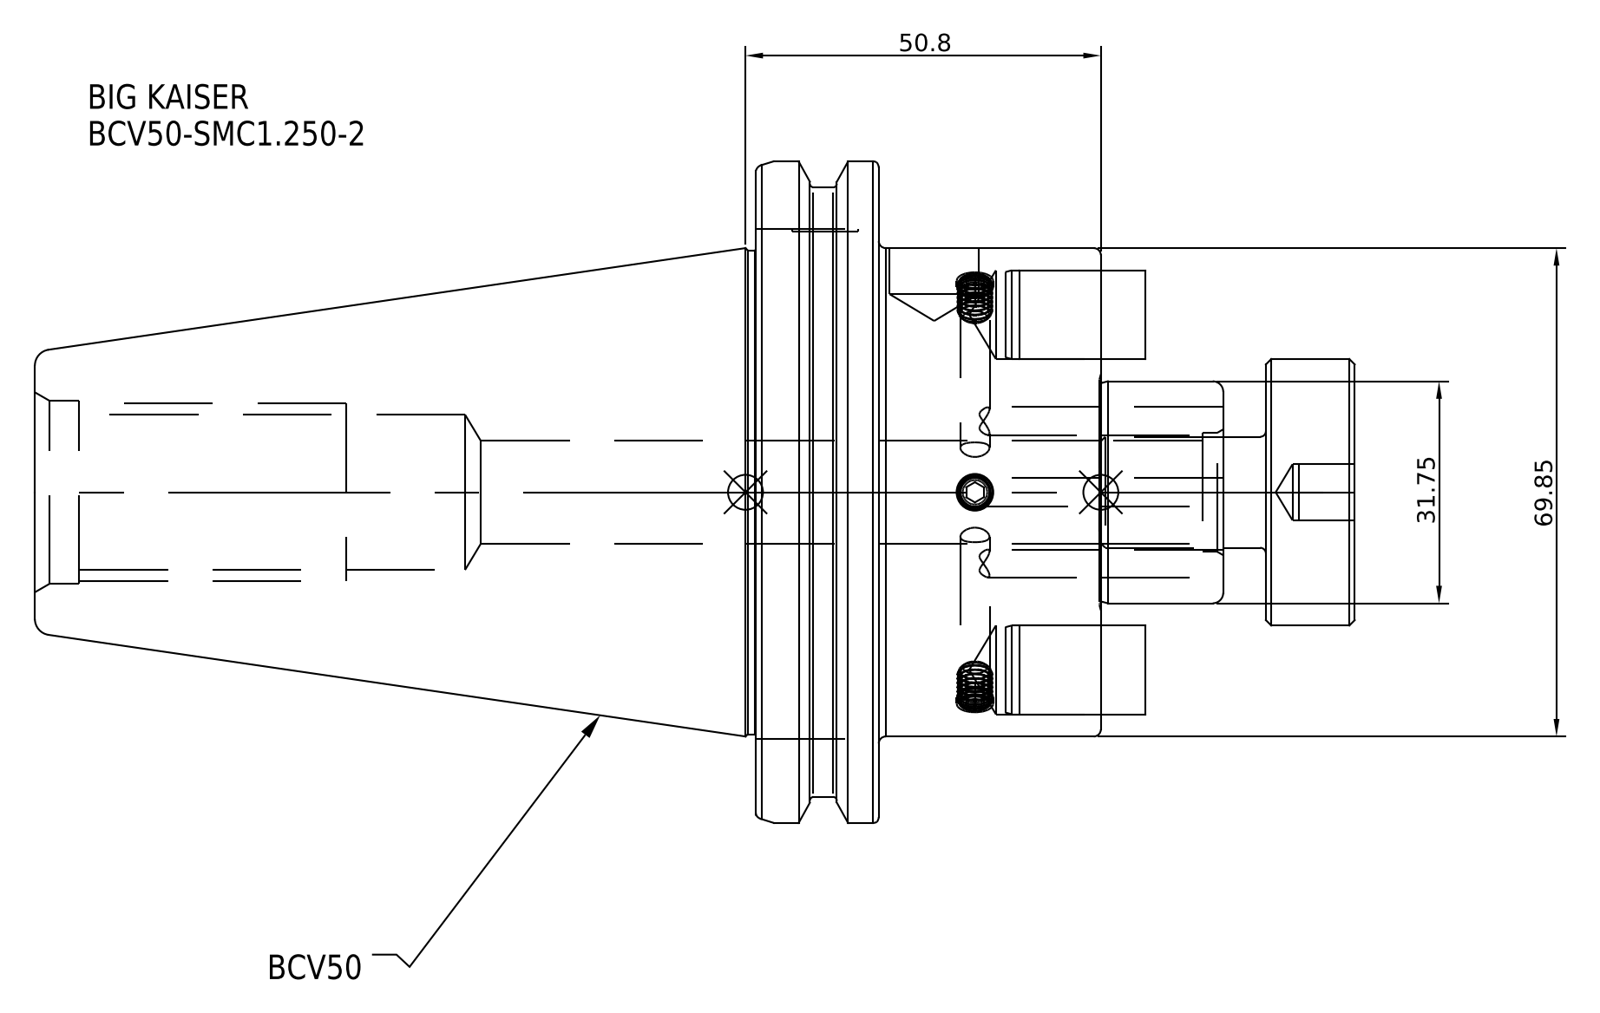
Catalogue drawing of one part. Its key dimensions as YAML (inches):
part_name: "BCV50-SMC1_250-2"
step_written_by: "SolidWorks 2021 (CONFIG_CONTROL_DESIGN)"
units: inches
bodies: {solids: 1, faces: 35, planar: 17, cylindrical: 12, other: 6}
overall_size: [6.252, 3.875, 3.875]
volume: 30.66
surface_area: 71.02
round_holes:
  - {diameter: 0.578, count: 1}
round_bosses_or_shafts:
  - {diameter: 3.875, count: 1}
  - {diameter: 3.594, count: 1}
  - {diameter: 2.75, count: 1}
face_to_face_distances: [0.691, 1.25, 1.941, 6, 4.75, 4.059, 0.5, 0.252, 1.502, 2.193]
